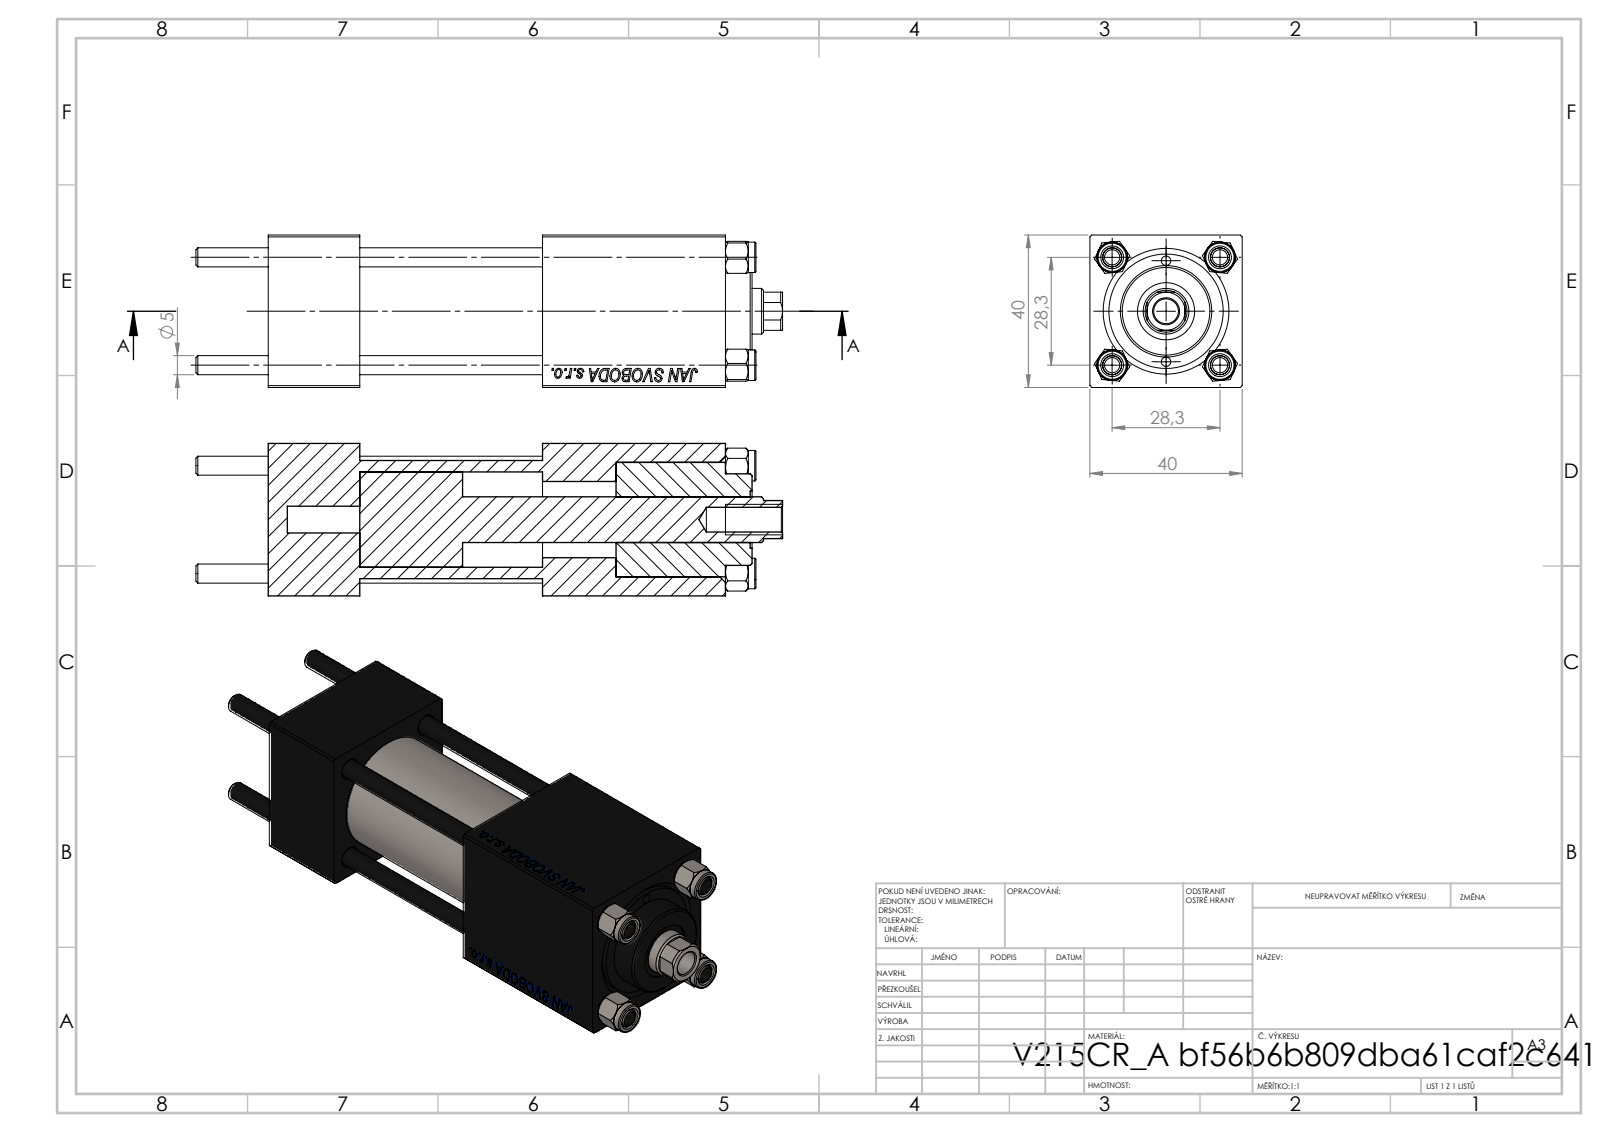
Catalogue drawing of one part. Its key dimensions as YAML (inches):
part_name: "CR025_012_A_0_G_A_G_M_020_+#_##_TYCINKA; NUT_M5; V215_VC_A; V215CR_VCP (+1 more)"
step_written_by: "SolidWorks 2019 (CONFIG_CONTROL_DESIGN)"
units: inches
bodies: {solids: 11, faces: 1137, planar: 519, cylindrical: 82, other: 536}
overall_size: [6.063, 1.575, 1.575]
volume: 8.862
surface_area: 91.8
round_holes:
  - {diameter: 0.197, count: 4}
  - {diameter: 0.787, count: 3}
  - {diameter: 0.098, count: 2}
  - {diameter: 0.276, count: 2}
  - {diameter: 0.518, count: 2}
  - {diameter: 0.256, count: 1}
  - {diameter: 0.472, count: 1}
  - {diameter: 0.591, count: 1}
  - {diameter: 0.984, count: 1}
  - {diameter: 1.181, count: 1}
round_bosses_or_shafts:
  - {diameter: 0.315, count: 4}
  - {diameter: 1.22, count: 1}
  - {diameter: 0.945, count: 1}
partial_cylinders:
  - {radius: 0.217, count: 1}
face_to_face_distances: [1.575, 1.89, 0.945, 3.594, 2.65, 4.724, 3.78, 1.13, 2.835, 0.76]
hole_center_spacings: [0.558, 0.788, 1.114, 1.214, 0.522, 1.576, 1.043, 2.874]
